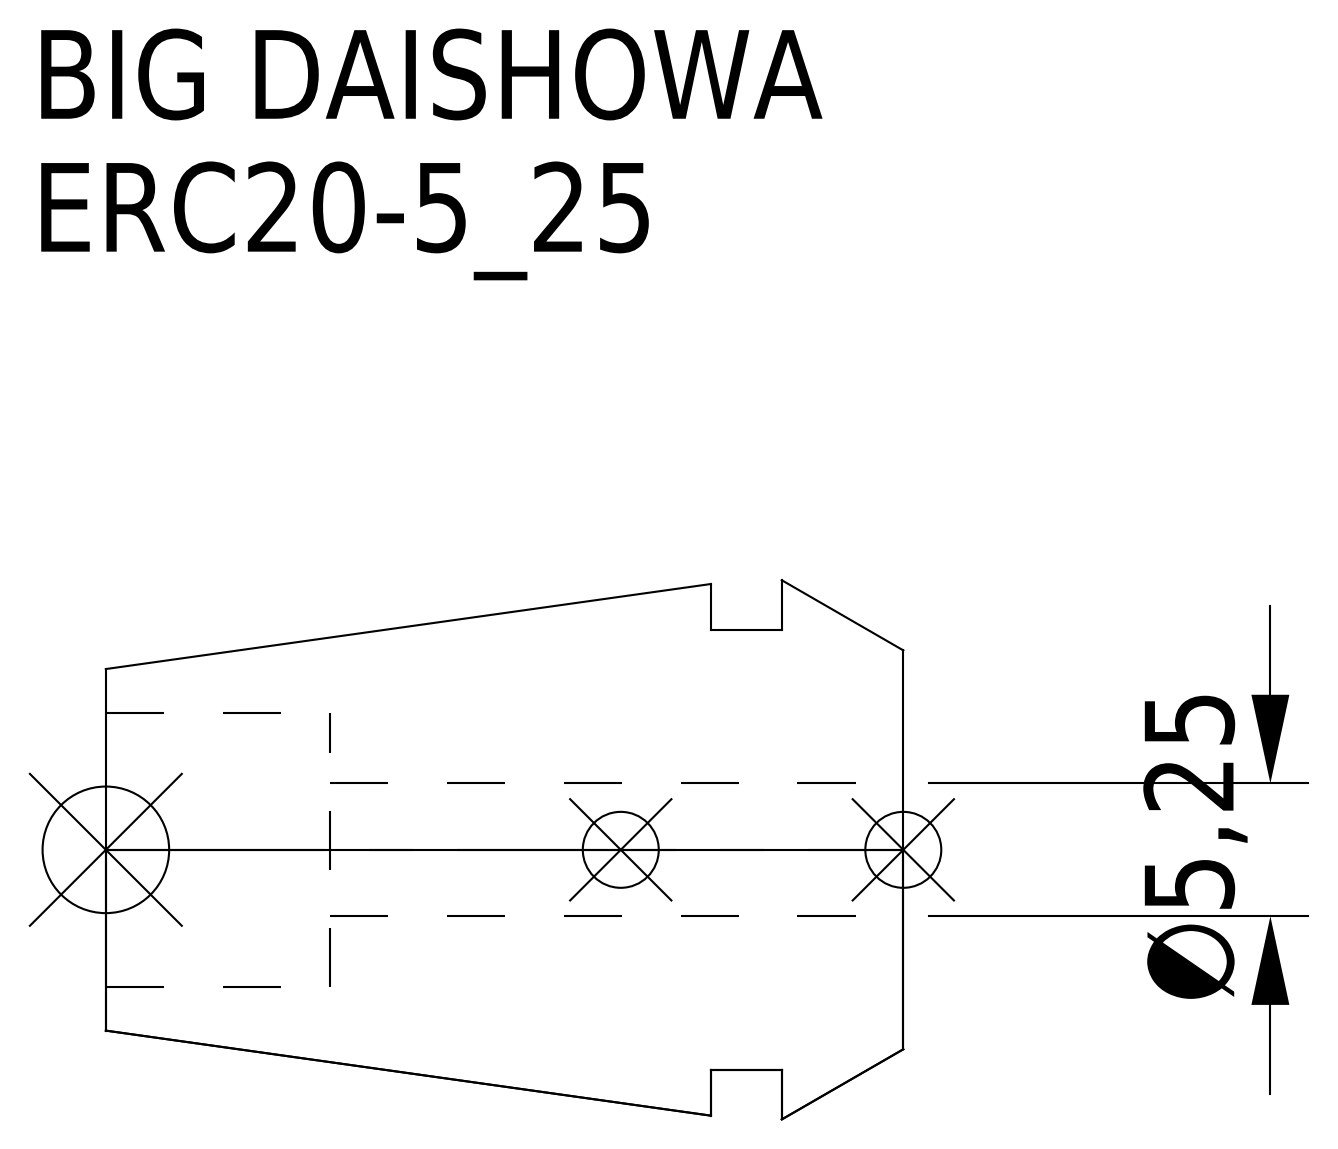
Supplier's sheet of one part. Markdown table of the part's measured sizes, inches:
| quantity | value |
| --- | --- |
| part name | ERC20-5_25 |
| STEP written by | CREO PARAMETRIC BY PTC INC, 2016380 (AUTOMOTIVE_DESIGN) |
| units | inches |
| bodies | 1 solid, 15 faces (5 planar, 6 cylindrical, 4 other) |
| overall size | 1.24 × 0.839 × 0.839 |
| volume | 0.402 in³ |
| surface area | 4.69 in² |
| round holes (diameter × count) | 0.207 × 1, 0.425 × 1 |
| round bosses / shafts (diameter × count) | 0.685 × 1 |
| main face-to-face distances | 0.189, 0.299, 0.11, 0.892, 0.703, 0.593, 1.24, 1.051, 0.941, 0.348 |
